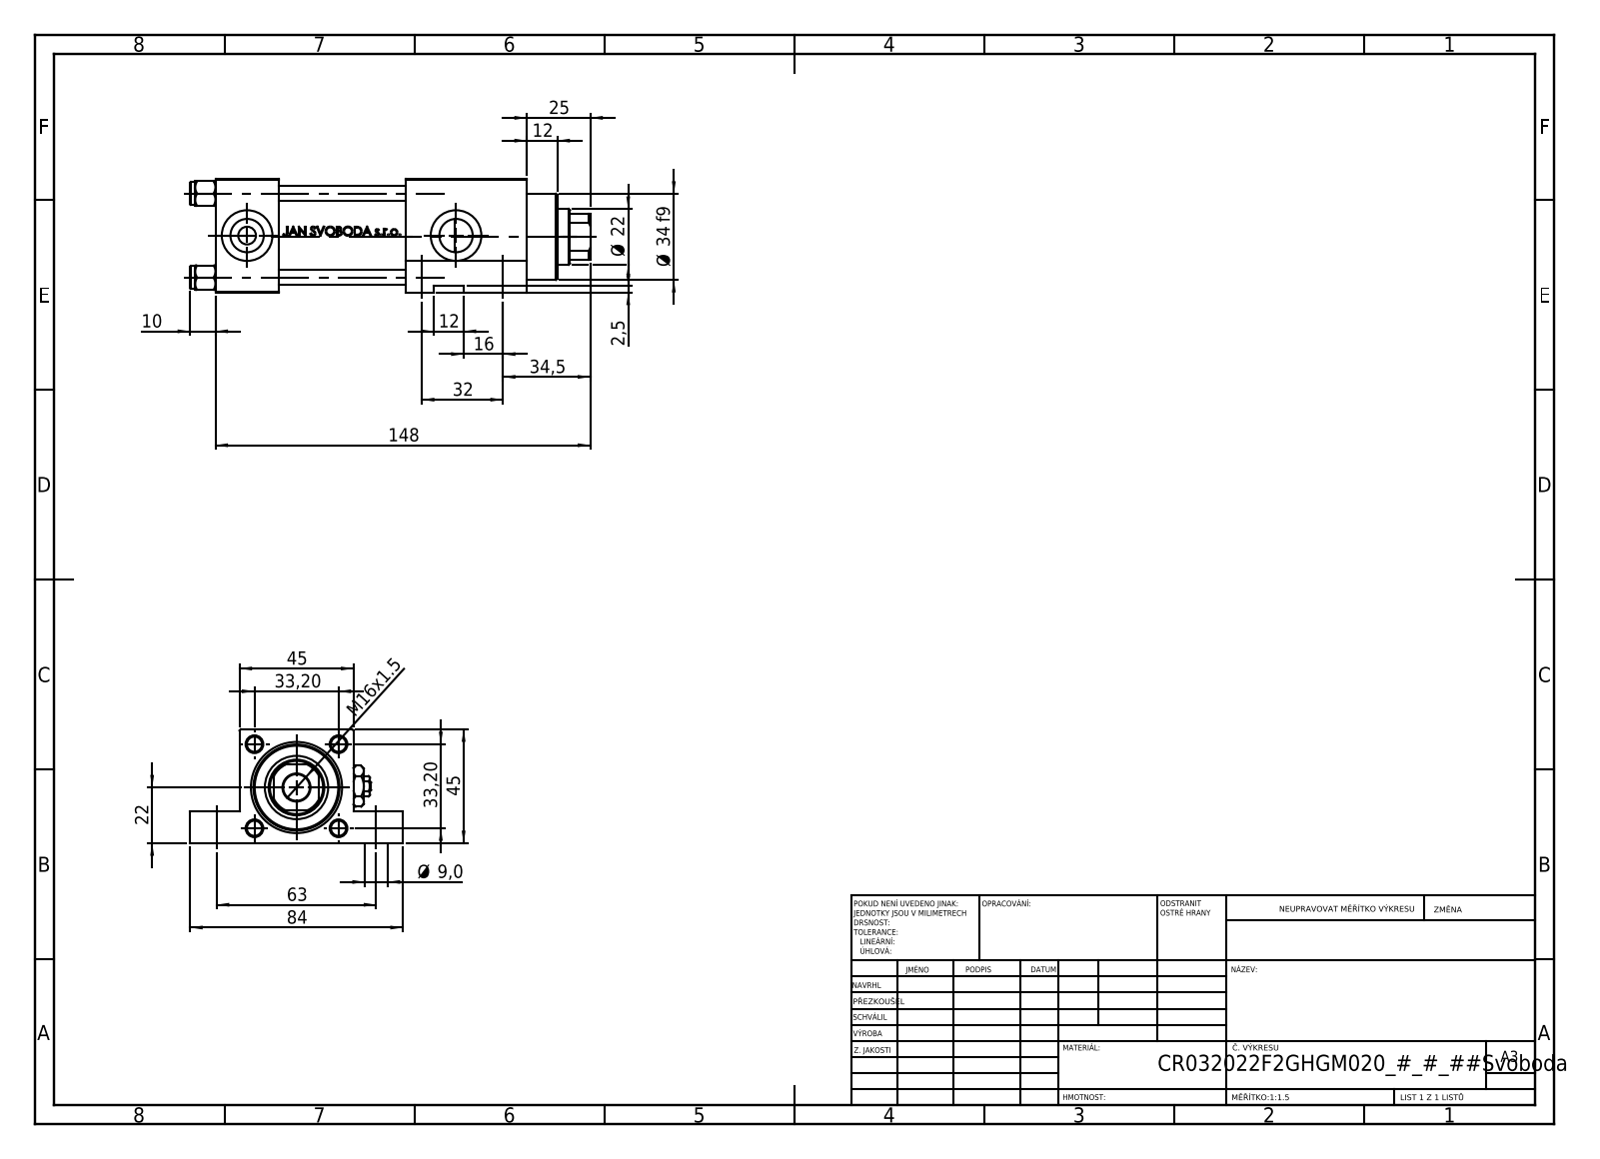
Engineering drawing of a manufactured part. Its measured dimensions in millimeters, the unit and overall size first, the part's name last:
Units: millimetres
Overall size (bounding box): 158 × 84 × 45
Round holes (diameter × count): ⌀6 ×4, ⌀9 ×4, ⌀7 ×2, ⌀13.16 ×2, ⌀20 ×2, ⌀10.5 ×1, ⌀13 ×1, ⌀22 ×1, ⌀24 ×1, ⌀25 ×1, ⌀32 ×1, ⌀33 ×1
Round bosses / shafts (diameter × count): ⌀9 ×4, ⌀38 ×1, ⌀34 ×1
Partial cylindrical surfaces — rounded edges, fillets, slot ends (radius × count): R10.5 ×1
Main face-to-face distances: 45, 25, 50, 98, 123, 75, 12.5, 32.5, 48, 10
Hole centre spacings: 33.2, 23.13, 23.83, 32, 46.95, 63, 70.66, 82.5
Volume: 227 061 mm³ · Surface area: 77 944 mm²
Bodies: 12 solids, 1150 faces (458 planar, 130 cylindrical, 562 other)
Part name (STEP PRODUCT): V215CR_F_Body; NUT_M5_F; V215CR_F_TYCINKA; V215CR_VCP_F (+2 more)
STEP written by: SolidWorks 2019 (CONFIG_CONTROL_DESIGN)
